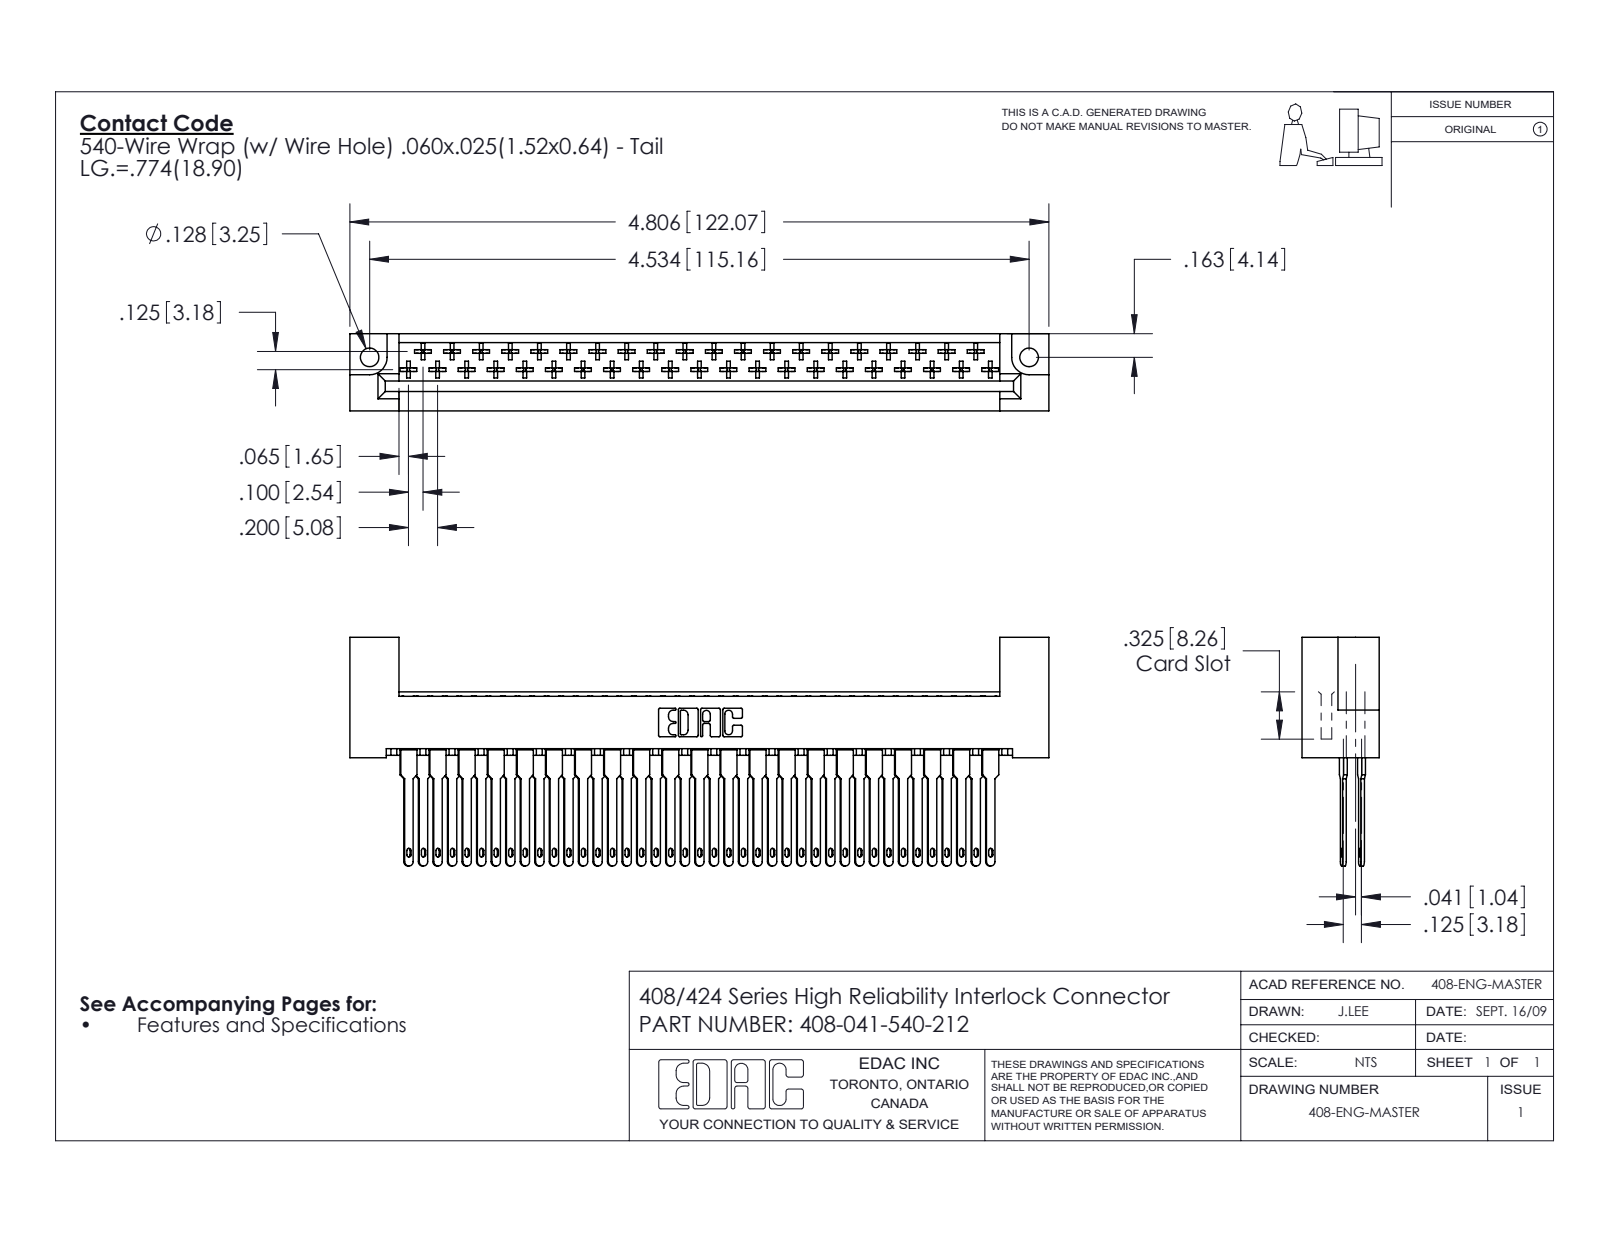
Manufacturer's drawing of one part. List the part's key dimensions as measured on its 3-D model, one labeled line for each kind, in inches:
Part name (STEP PRODUCT): 408-047-540-212; 408-290-001_408-290-140; 408 Part_041 - 2
STEP written by: SolidWorks 2016 (CONFIG_CONTROL_DESIGN)
Units: inches
Bodies: 42 solids, 2476 faces (1811 planar, 501 cylindrical, 164 other)
Overall size (bounding box): 4.806 × 1.572 × 0.531
Volume: 0.962 in³ · Surface area: 32.09 in²
Round holes (diameter × count): ⌀0.128 ×2
Partial cylindrical surfaces — rounded edges, fillets, slot ends (radius × count): R0.01 ×246, R0.015 ×82, R0.02 ×43, R0.03 ×41, R0.01 ×22, R0.007 ×6, R0.031 ×6, R0.026 ×3
Main face-to-face distances: 0.531, 0.125, 0.1, 0.025, 0.025, 0.361, 0.235, 0.259, 0.217, 0.272
Hole centre spacings: 4.534
